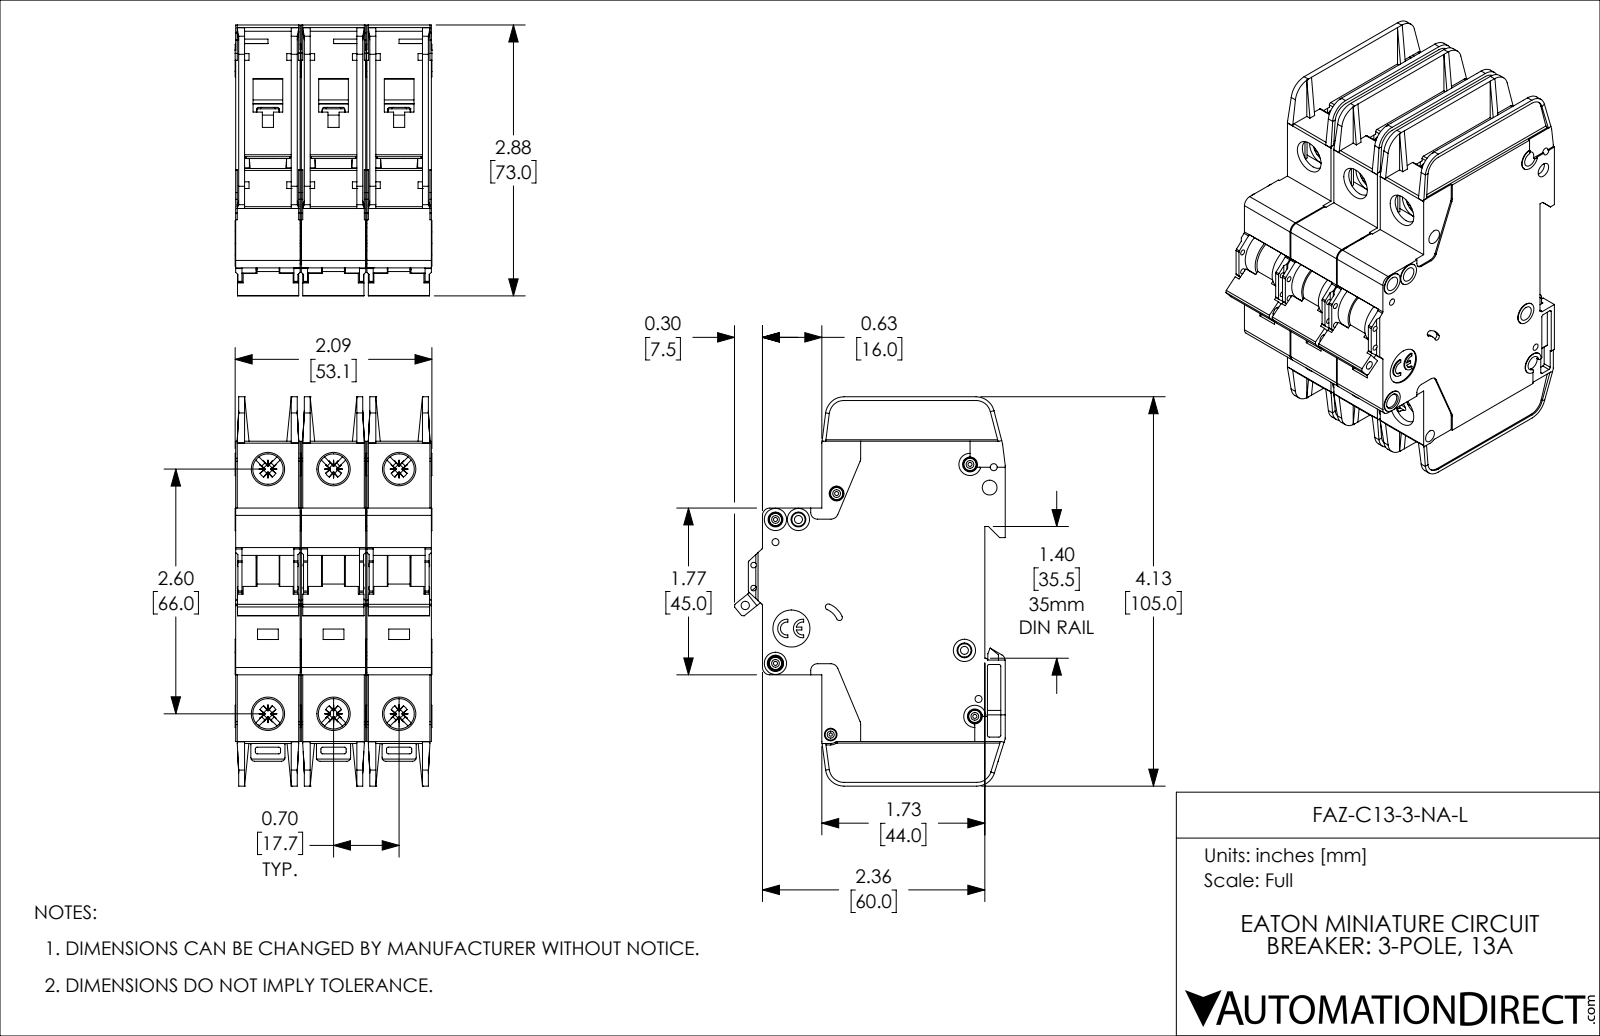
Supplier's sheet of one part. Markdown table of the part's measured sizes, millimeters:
| quantity | value |
| --- | --- |
| part name | FAZ-C13-3-NA-L |
| STEP written by | SolidWorks 2019 (AUTOMOTIVE_DESIGN) |
| units | millimeters |
| bodies | 3 solids, 3381 faces (2013 planar, 1071 cylindrical, 297 other) |
| overall size | 105 × 73.1 × 53.1 |
| volume | 230 200 mm³ |
| surface area | 79 350 mm² |
| round holes (diameter × count) | 4 × 8, 8.2 × 6, 1.1 × 5, 1.9 × 4, 1.5 × 2, 2.2 × 2, 0.9 × 1, 2.3 × 1, 2.5 × 1, 3.4 × 1, 10 × 1 |
| round bosses / shafts (diameter × count) | 3.3 × 5, 6 × 4, 3 × 4, 2.5 × 3 |
| partial cylindrical surfaces (radius × count) | 0.5 × 72, 0.4 × 30, 1 × 18, 1.1 × 12, 2 × 12, 0.2 × 6, 0.3 × 6, 0.7 × 6 |
| main face-to-face distances | 17.7, 1.2, 35.4, 17.4, 15, 35.1, 18.9, 16.5, 2.7, 2.4 |
| hole center spacings | 17.7, 68.3, 66, 6.2, 13.6, 22.1, 35.4, 74.9 |
